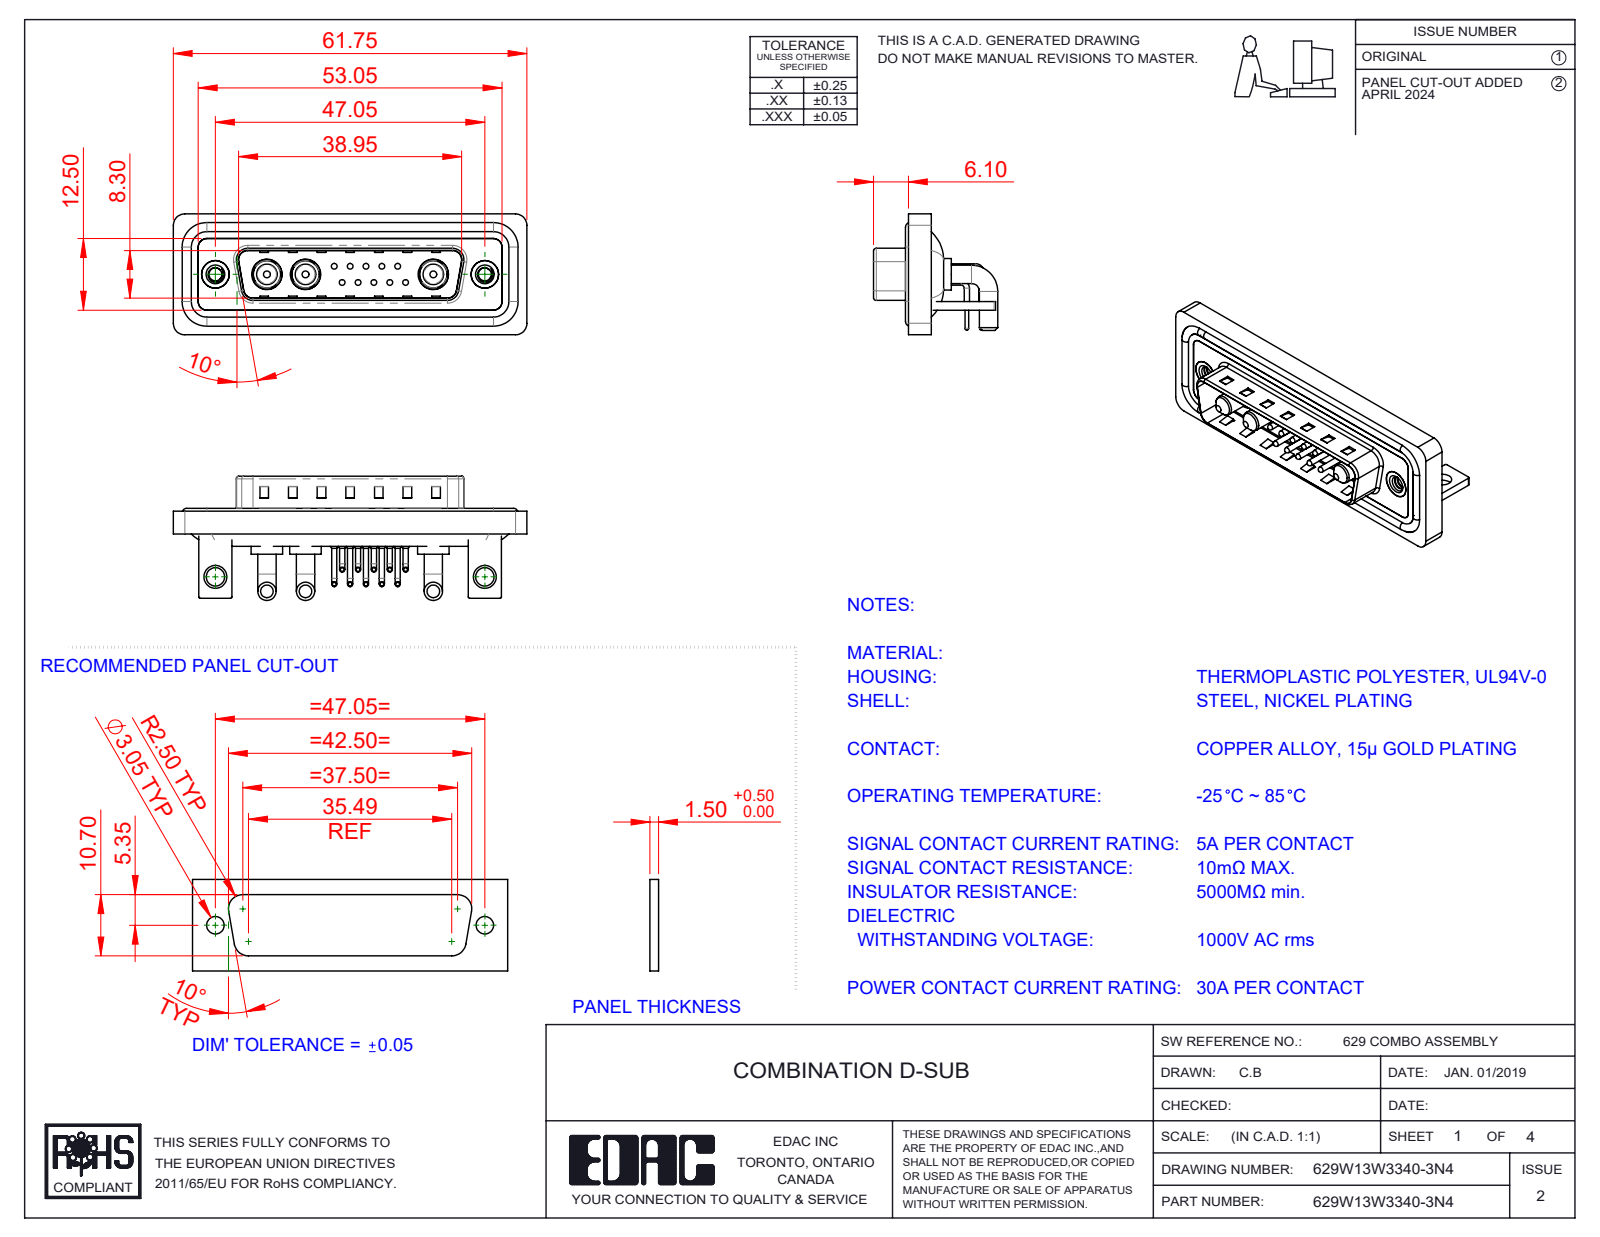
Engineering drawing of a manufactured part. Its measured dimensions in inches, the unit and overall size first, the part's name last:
Units: inches
Overall size (bounding box): 2.431 × 0.854 × 0.831
Round holes (diameter × count): ⌀0.03 ×10, ⌀0.063 ×10, ⌀0.079 ×10, ⌀0.191 ×3, ⌀0.209 ×3, ⌀0.089 ×2, ⌀0.126 ×2, ⌀0.157 ×2, ⌀0.189 ×2, ⌀0.197 ×2
Round bosses / shafts (diameter × count): ⌀0.035 ×20, ⌀0.059 ×10, ⌀0.039 ×10, ⌀0.026 ×10, ⌀0.126 ×6, ⌀0.063 ×4, ⌀0.217 ×3, ⌀0.205 ×3
Partial cylindrical surfaces — rounded edges, fillets, slot ends (radius × count): R0.079 ×19, R0.059 ×18, R0.01 ×16, R0.04 ×10, R0.02 ×9, R0.063 ×8, R0.024 ×4, R0.026 ×4
Main face-to-face distances: 0.016, 0.031, 0.059, 0.114, 0.083, 0.043, 0.161, 0.063, 0.146, 0.177
Hole centre spacings: 0.124, 0.109, 0.198, 0.218, 0.295, 0.198, 0.327, 0.398
Volume: 0.486 in³ · Surface area: 20.36 in²
Bodies: 25 solids, 1752 faces (899 planar, 629 cylindrical, 224 other)
Part name (STEP PRODUCT): 629Combo Contact Row 1; 629Combo Housing_13W3; 629W13W3340-3N4; 629Combo Shell Rear_25 Contacts (+6 more)
STEP written by: SolidWorks 2023 (CONFIG_CONTROL_DESIGN)
